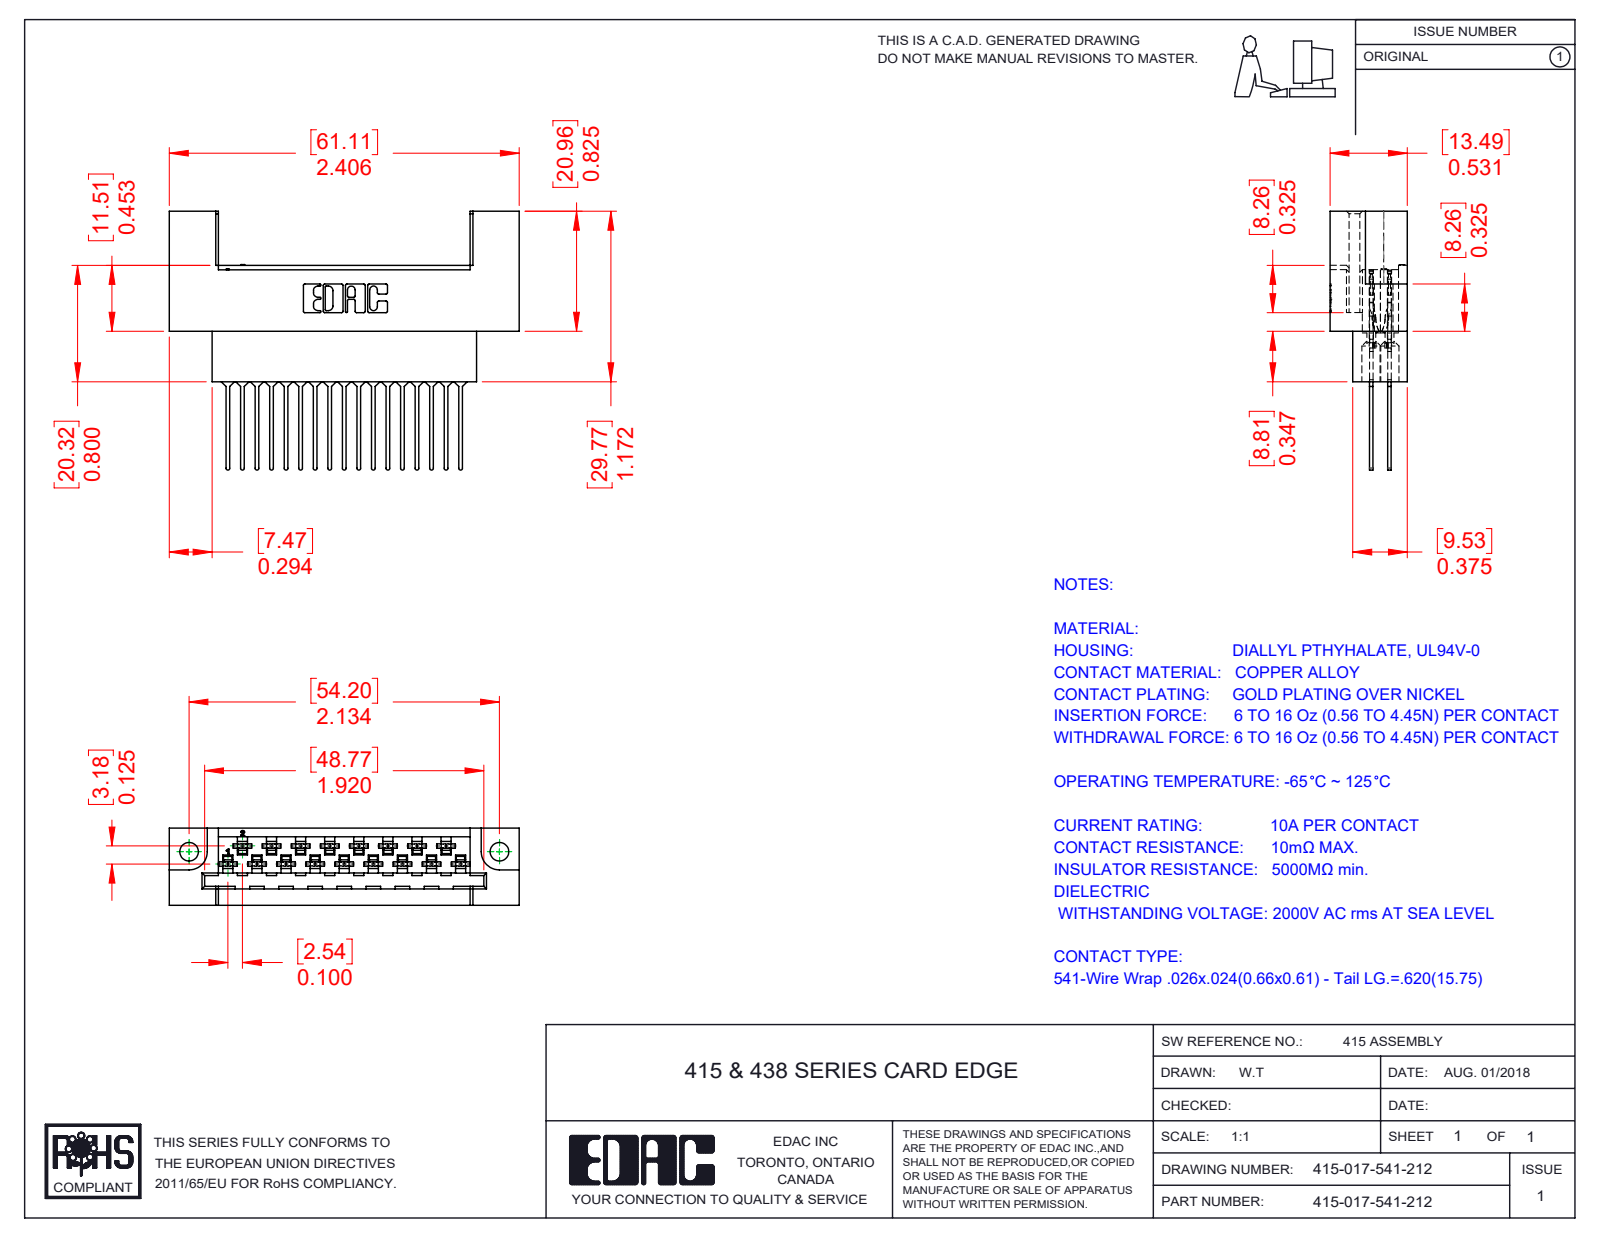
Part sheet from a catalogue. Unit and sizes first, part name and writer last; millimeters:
Units: millimetres
Overall size (bounding box): 61.11 × 45.17 × 13.49
Round holes (diameter × count): ⌀1.27 ×17, ⌀3.3 ×17, ⌀3.25 ×2
Partial cylindrical surfaces — rounded edges, fillets, slot ends (radius × count): R0.3 ×68, R0.56 ×68, R0.18 ×34, R0.2 ×34, R0.41 ×34, R2.03 ×34, R0.25 ×22, R0.33 ×17
Main face-to-face distances: 3.18, 0.61, 13.49, 1.88, 7.49, 1.27, 6.61, 6.88, 6, 3.58
Hole centre spacings: 5.08, 10.16, 15.24, 20.32, 2.54, 4.06, 7.62, 8.25
Volume: 11 168 mm³ · Surface area: 12 926 mm²
Bodies: 18 solids, 1826 faces (1163 planar, 488 cylindrical, 175 other)
Part name (STEP PRODUCT): 415-210-001_415-210-017-212; 415-017-541-212; 516-290-001_541
STEP written by: SolidWorks 2016 (CONFIG_CONTROL_DESIGN)
